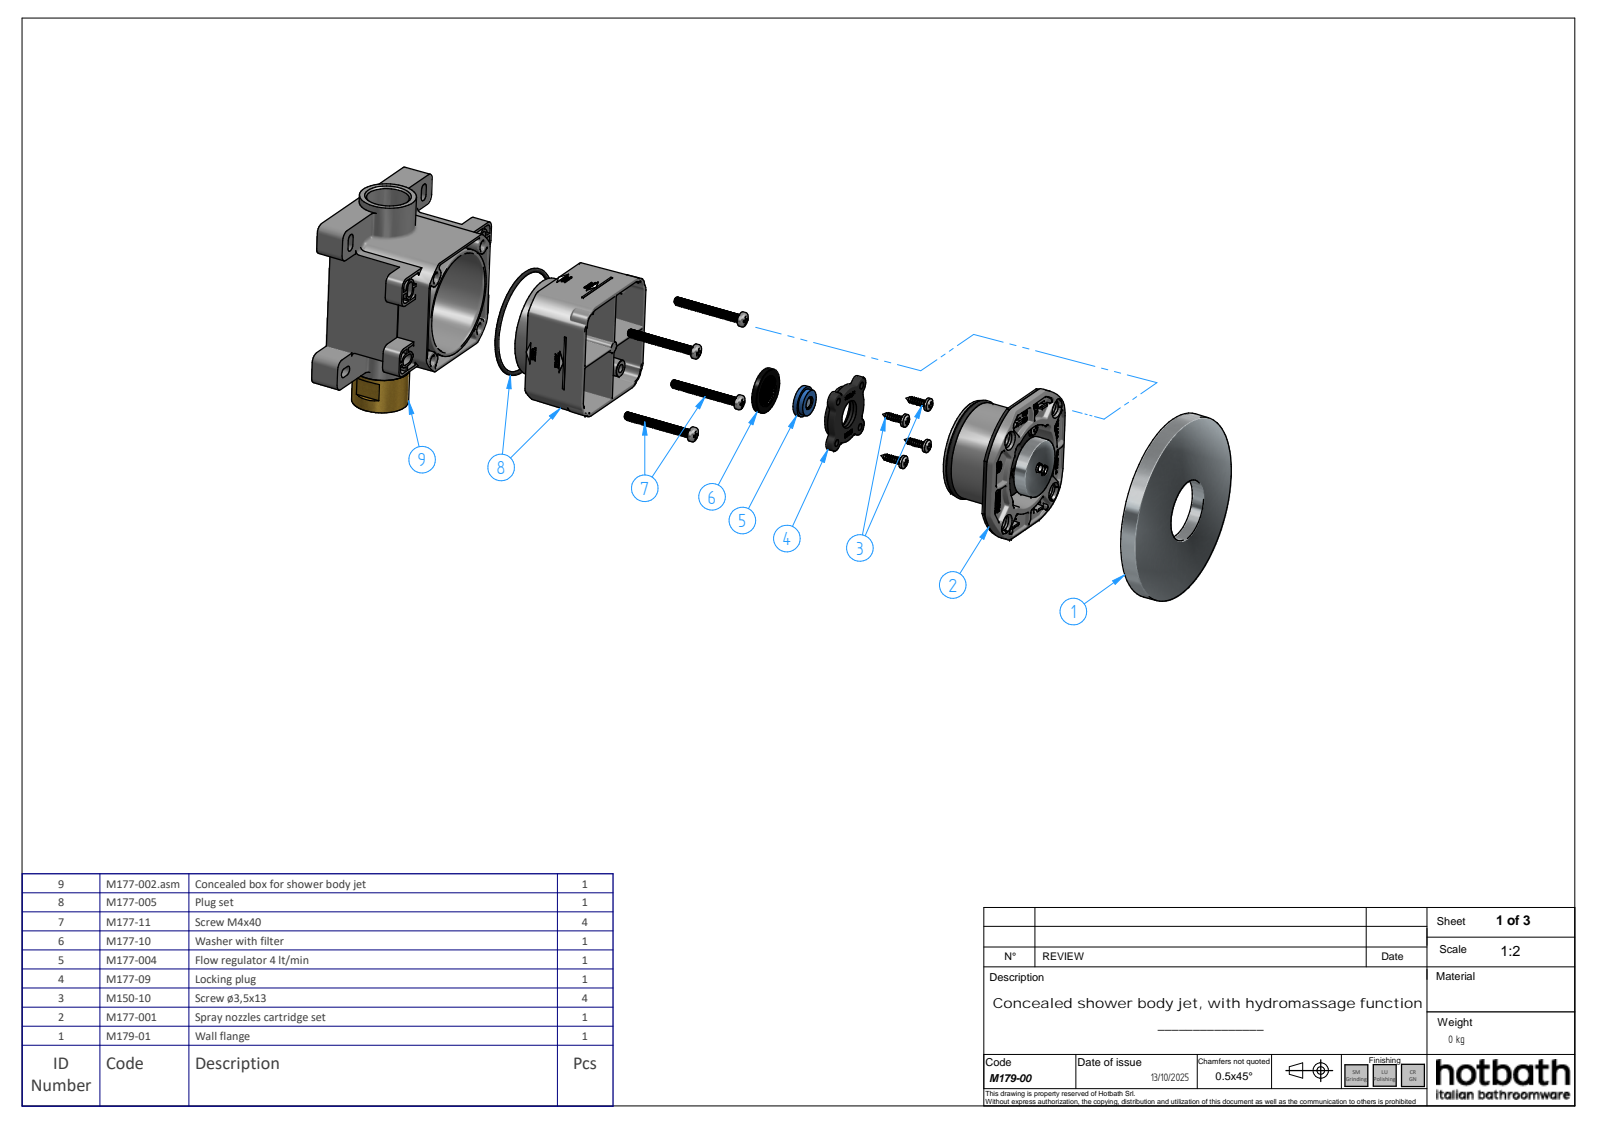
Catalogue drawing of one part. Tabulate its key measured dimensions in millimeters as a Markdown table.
| quantity | value |
| --- | --- |
| part name | M179-00; M177-001_oa_0; A032016_16800ZZ_oa_1; A019020_00701ZZ_oa_2 (+1 more) |
| STEP written by | Solid Edge (AUTOMOTIVE_DESIGN) |
| units | millimeters |
| bodies | 4 solids, 1106 faces (453 planar, 259 cylindrical, 394 other) |
| overall size | 100 × 100 × 13.13 |
| volume | 23 603 mm³ |
| surface area | 24 093 mm² |
| round holes (diameter × count) | 1.8 × 2, 2.6 × 2, 6 × 2, 29.85 × 1, 97 × 1 |
| partial cylindrical surfaces (radius × count) | 0.2 × 32, 0.1 × 18, 0.5 × 8, 1.2 × 8, 2 × 8, 0.12 × 6, 0.46 × 5, 0.11 × 4 |
| main face-to-face distances | 77.8, 8.9, 4.4, 4.5, 4.7, 4.2, 63.6, 2, 65.6, 60.8 |
| hole center spacings | 11.5, 15.91, 10.97, 11, 11.3, 11.7, 19.53, 23 |
